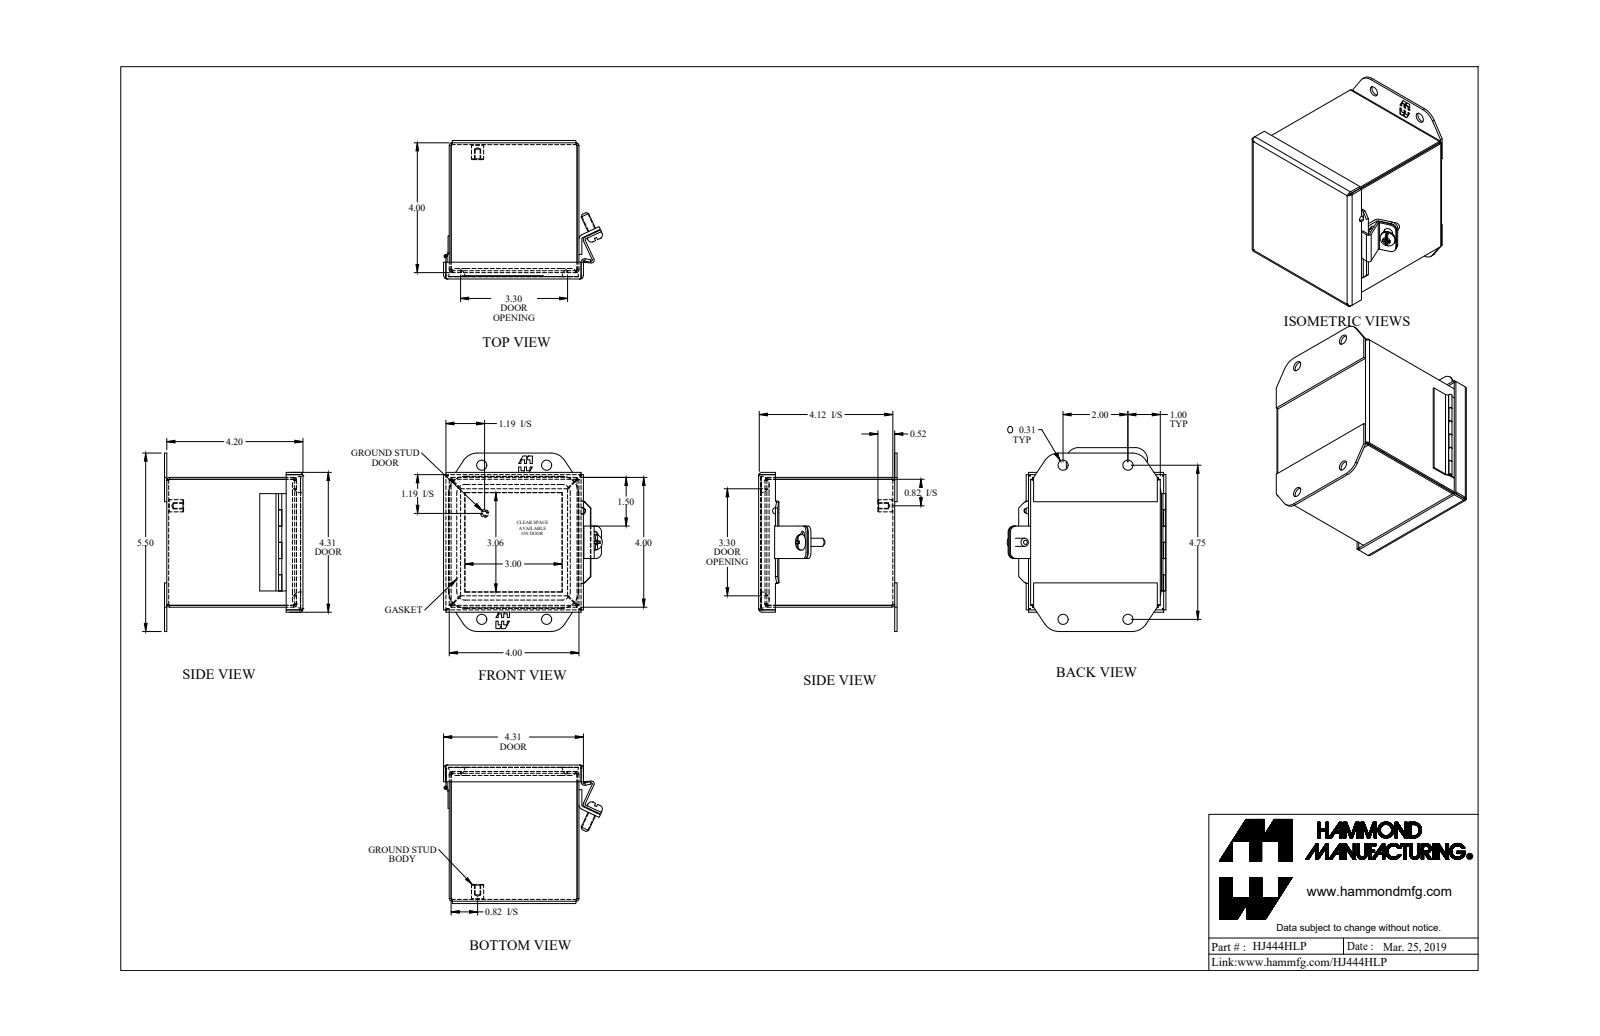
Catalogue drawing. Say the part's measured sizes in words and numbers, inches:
The part is named "HJ444HLP". Its 3-D file was written by "SolidWorks 2018 (AUTOMOTIVE_DESIGN)". It is 13 solids with 490 faces: 283 planar, 129 cylindrical and 78 other. Overall it measures 5.5 by 4.896 by 4.269 inches. Its volume is 9.012 cubic inches and its surface area 289.7 square inches. Round holes: 4 of diameter 0.313, 1 of diameter 0.05, 1 of diameter 0.156, 1 of diameter 0.213. Round bosses or shafts: 2 of diameter 0.25, 1 of diameter 0.48, 1 of diameter 0.375, 1 of diameter 0.188, 1 of diameter 0.1, 1 of diameter 0.045. Partial cylindrical surfaces (rounded edges, fillets, slot ends): 14 of radius 0.188, 10 of radius 0.029, 10 of radius 0.086, 5 of radius 0.036, 5 of radius 0.108, 4 of radius 0.25, 4 of radius 0.499, 4 of radius 0.5. The main face-to-face distances are 0.057, 3.943, 0.072, 4, 3.886, 4.197, 4.125, 0.057, 4.068, 4.14. The hole center spacings are 2, 4.75, 5.154, 1.257, 2.466, 3.502, 4.094.
